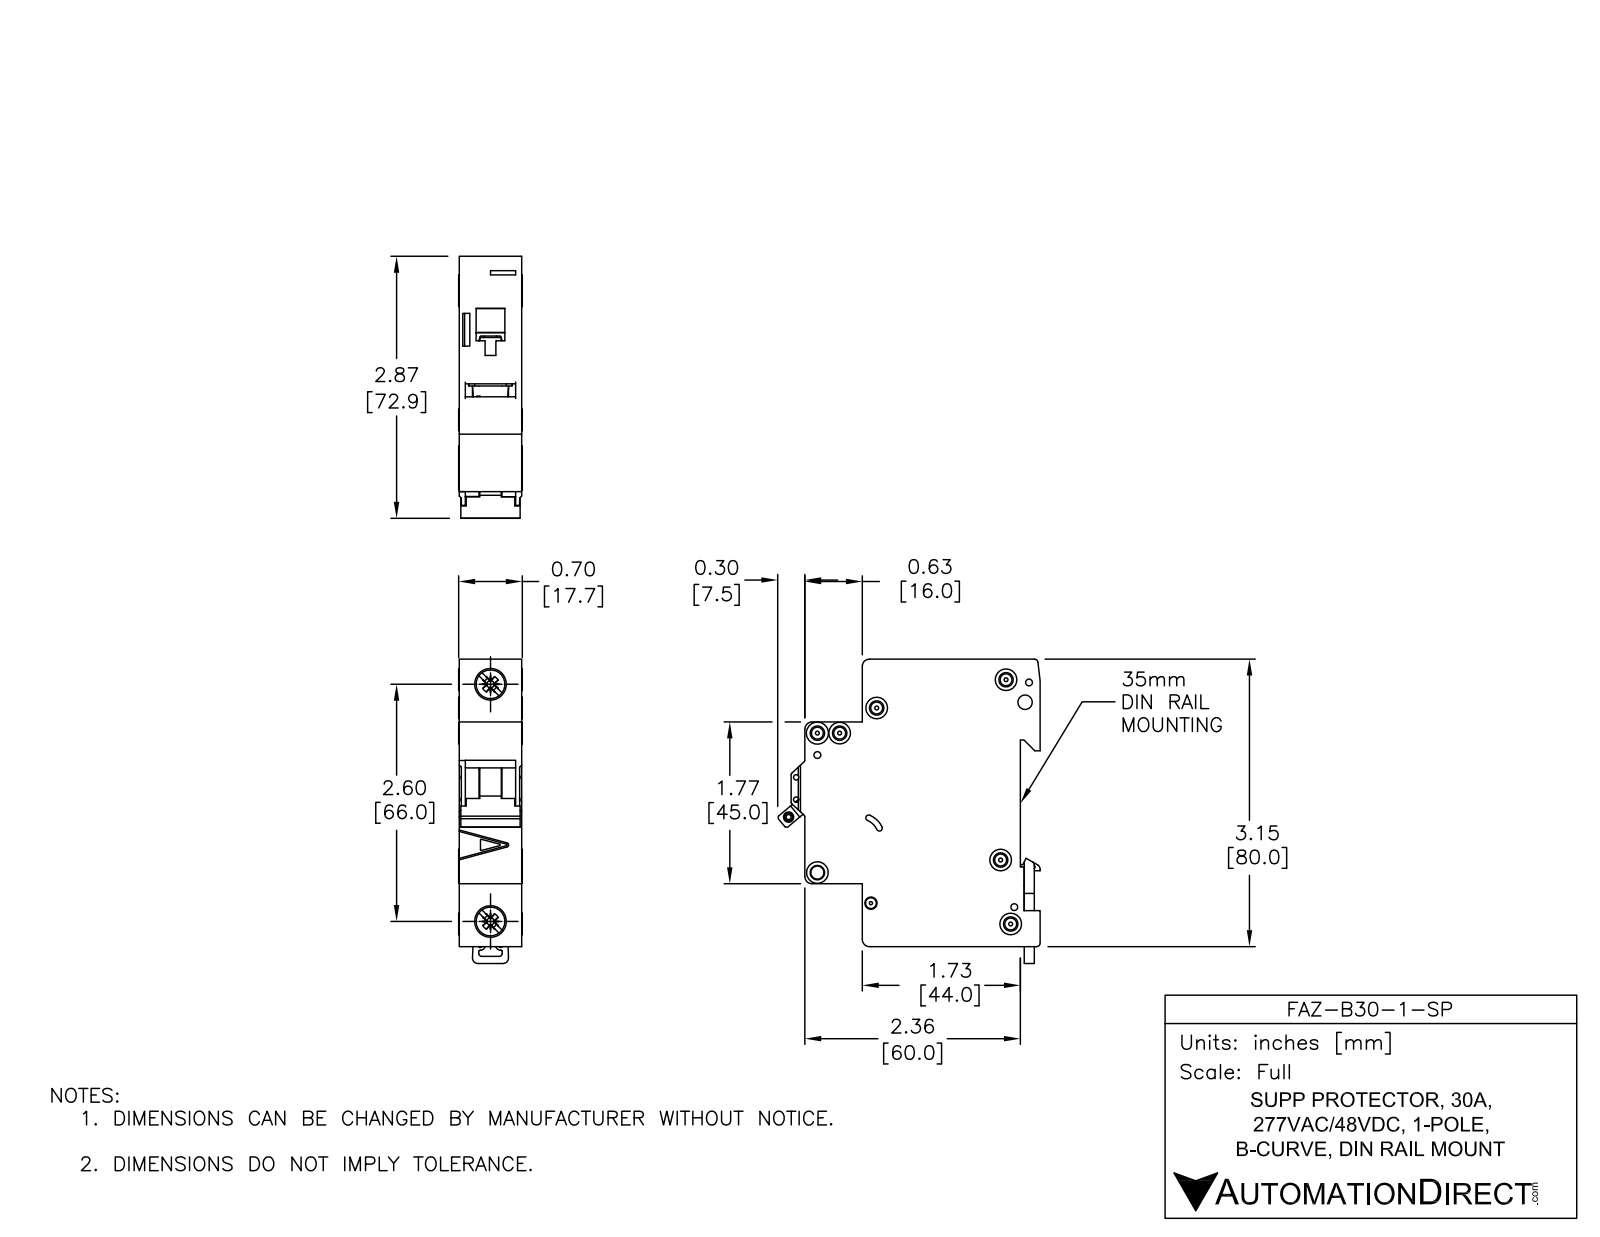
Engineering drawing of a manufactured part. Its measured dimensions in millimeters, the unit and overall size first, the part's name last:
Units: millimetres
Overall size (bounding box): 84.78 × 73.04 × 17.7
Round holes (diameter × count): ⌀3.6 ×6, ⌀1.9 ×3, ⌀1.09 ×2, ⌀1.5 ×2, ⌀4 ×2, ⌀7.15 ×2, ⌀2.15 ×1, ⌀2.2 ×1, ⌀2.55 ×1, ⌀3.3 ×1, ⌀3.4 ×1
Round bosses / shafts (diameter × count): ⌀6 ×4, ⌀8.2 ×2, ⌀2.5 ×1
Partial cylindrical surfaces — rounded edges, fillets, slot ends (radius × count): R0.25 ×30, R0.5 ×13, R2 ×8, R0.2 ×5, R1 ×4, R0.8 ×2, R3 ×2, R1.5 ×1
Main face-to-face distances: 17.5, 79.48, 5.5, 49.5, 44, 65.5, 60, 16, 1.75, 15.75
Hole centre spacings: 6.2, 13.64, 4.81, 5.19, 5.61, 6.1, 6.44, 8.19
Volume: 74 935 mm³ · Surface area: 19 545 mm²
Bodies: 5 solids, 558 faces (235 planar, 202 cylindrical, 121 other)
Part name (STEP PRODUCT): FAZ-B30-1-SP
STEP written by: SolidWorks 2014 (AUTOMOTIVE_DESIGN)
